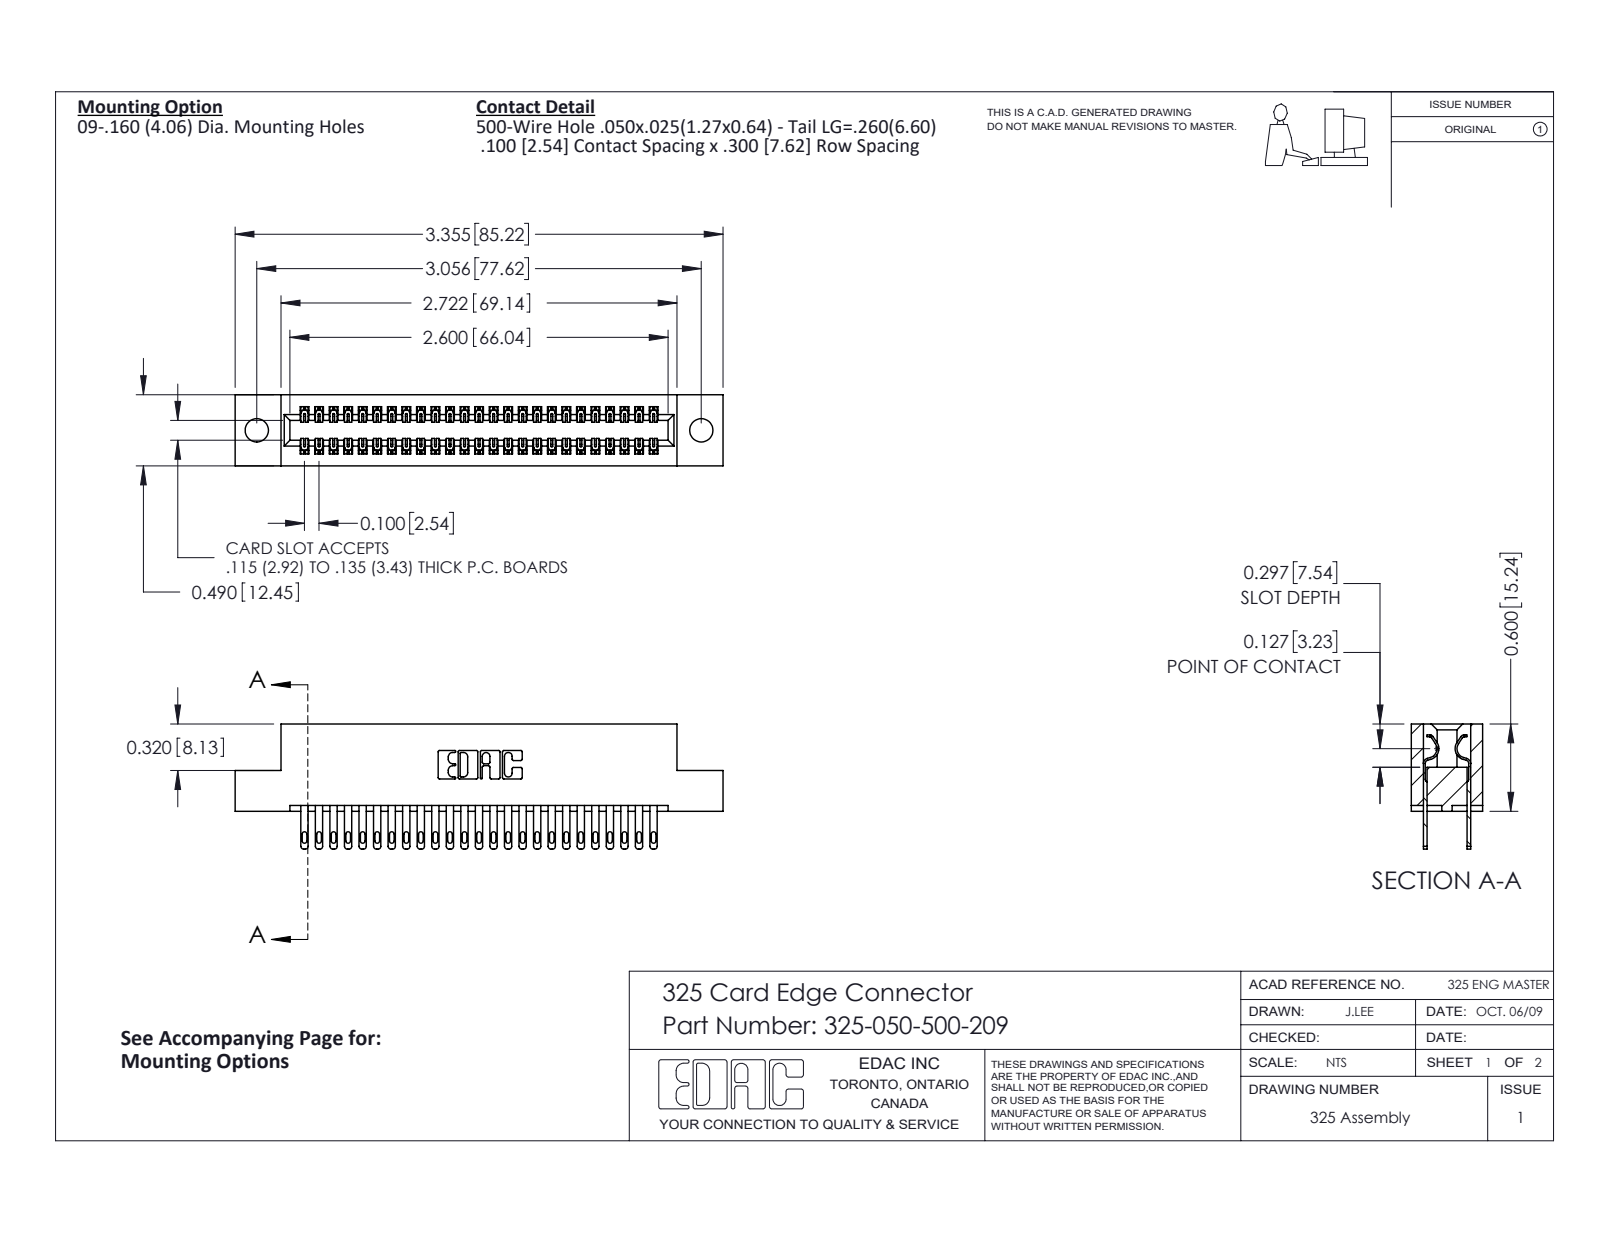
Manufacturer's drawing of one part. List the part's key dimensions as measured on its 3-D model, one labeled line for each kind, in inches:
Part name (STEP PRODUCT): 325-292-001_325-293-100; 325-050-500-209; 325 Part_.160 TH
STEP written by: SolidWorks 2016 (CONFIG_CONTROL_DESIGN)
Units: inches
Bodies: 51 solids, 2514 faces (1570 planar, 944 cylindrical, 0 other)
Overall size (bounding box): 3.355 × 0.86 × 0.49
Volume: 0.657 in³ · Surface area: 20.27 in²
Round holes (diameter × count): ⌀0.16 ×2
Partial cylindrical surfaces — rounded edges, fillets, slot ends (radius × count): R0.006 ×75, R0.016 ×50, R0.02 ×50, R0.01 ×22, R0.007 ×6, R0.031 ×6, R0.026 ×3, R0.014 ×2
Main face-to-face distances: 0.083, 0.407, 0.3, 0.107, 0.383, 0.025, 0.49, 0.325, 0.275, 0.04
Hole centre spacings: 3.056
